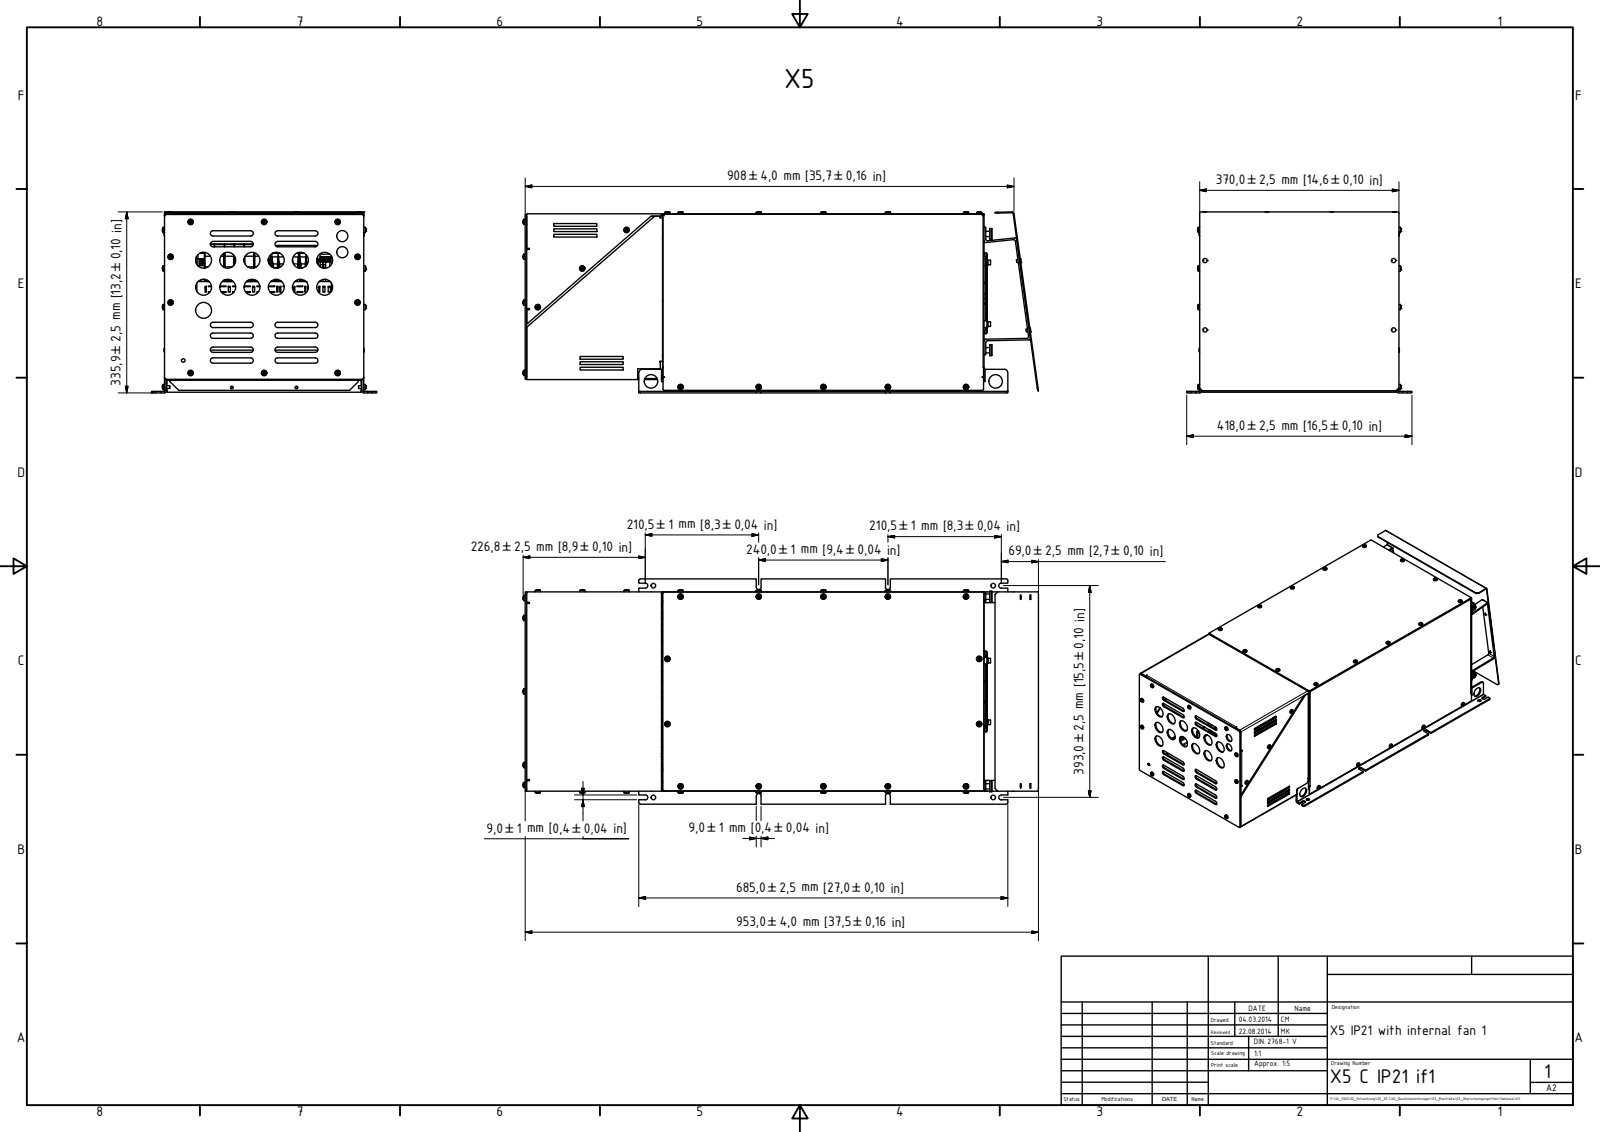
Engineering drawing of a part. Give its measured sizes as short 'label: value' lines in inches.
name: 10100398 Deckel X5_X6; 10100399 Seitenwand X5; 10100396 Anschlussblech X5; 10100397 Lüfterblech X5 (+8 more)
written by: Autodesk Inventor 2015 (AUTOMOTIVE_DESIGN)
unit: in
bodies: 137 solids, 8031 faces (5077 planar, 1957 cylindrical, 997 other)
size: 37.67 × 16.457 × 13.241
volume: 229.5 in³; area: 6 050 in²
holes: 42× ⌀0.163, 32× ⌀0.256, 14× ⌀0.268, 13× ⌀0.157, 13× ⌀0.217, 13× ⌀1.161, 8× ⌀0.354, 7× ⌀0.128, 6× ⌀0.236, 6× ⌀0.335, 6× ⌀0.433, 5× ⌀0.276
bosses: 44× ⌀0.197, 42× ⌀0.181, 8× ⌀0.055, 7× ⌀0.157, 6× ⌀0.394, 6× ⌀0.315, 5× ⌀0.335, 4× ⌀0.787
rounds: 112× R0.009, 58× R0.02, 50× R0.079, 37× R0.004, 29× R0.004, 28× R0.217, 25× R0.197, 24× R0.03
face distances: 0.039, 0.079, 14.528, 14.488, 0.118, 14.567, 0.059, 12.037, 14.449, 12.165
hole spacings: 4.724, 13.858, 13.78, 5.709, 10.433, 15.157, 4.311, 0.374
